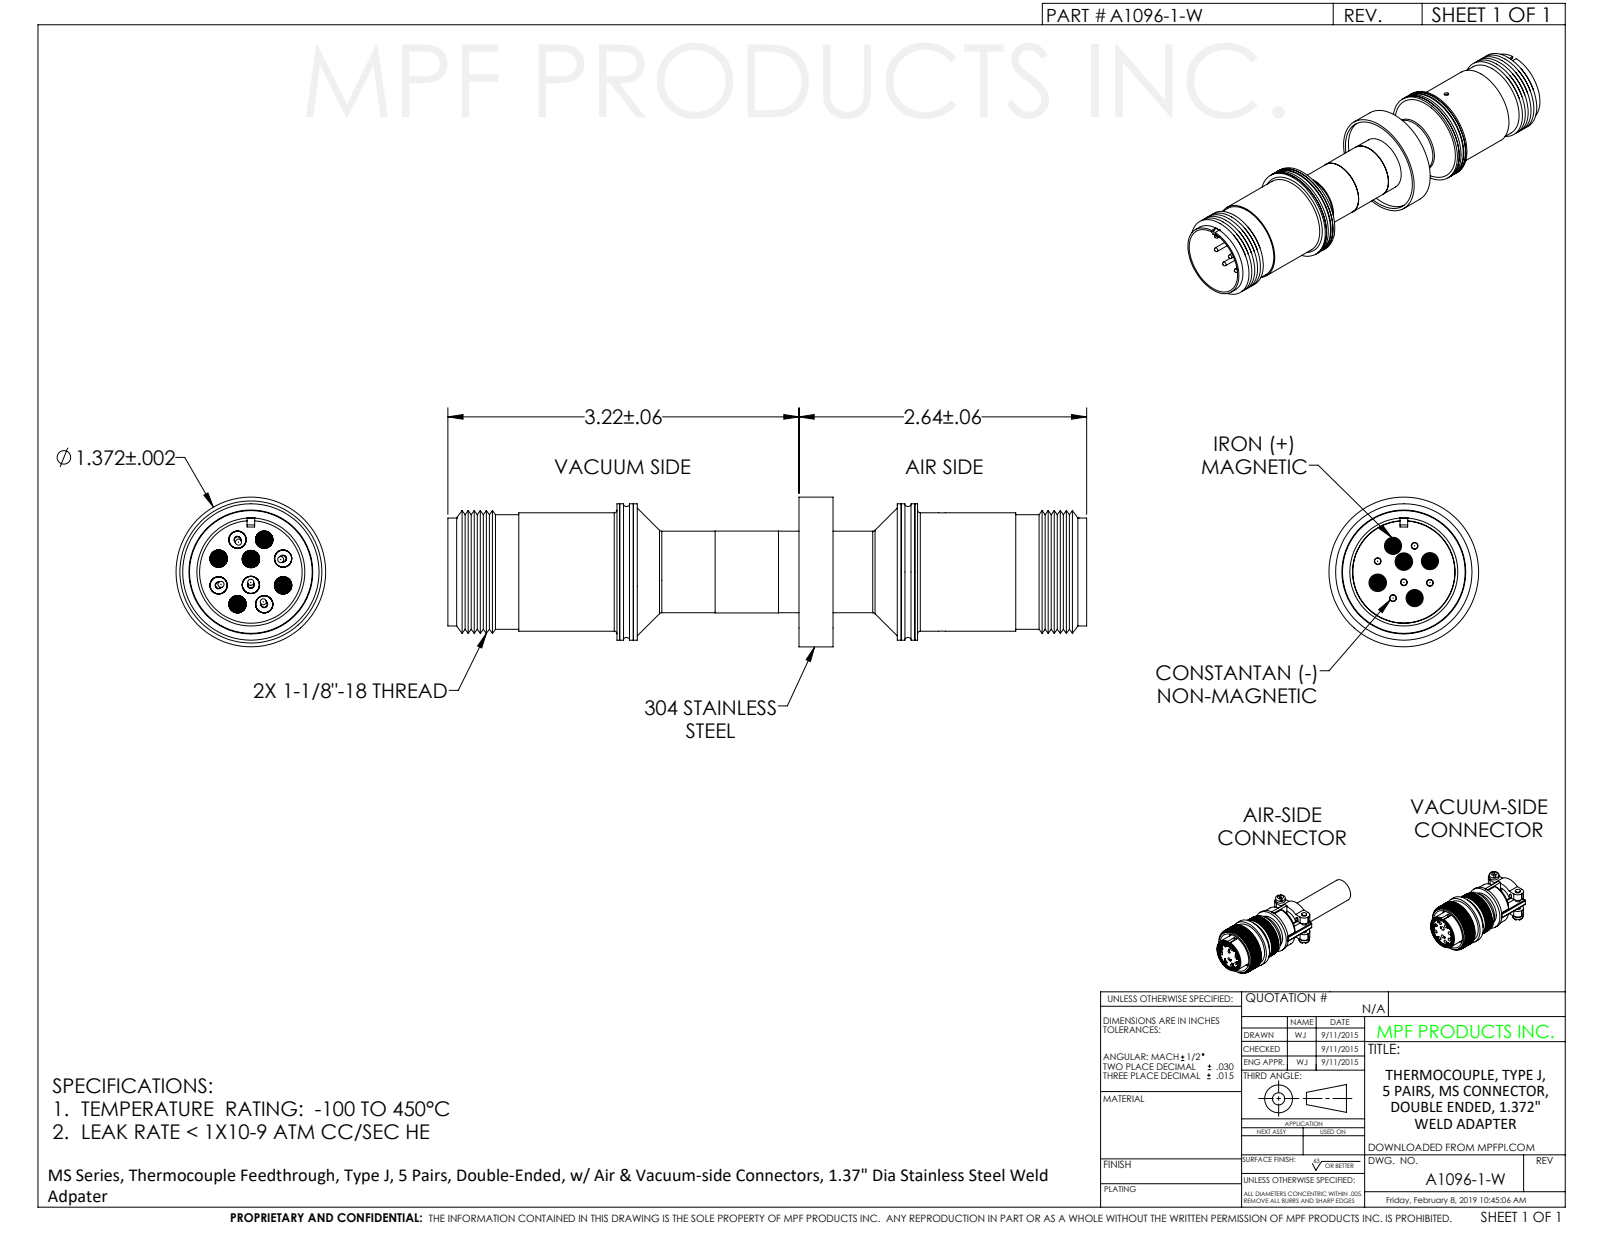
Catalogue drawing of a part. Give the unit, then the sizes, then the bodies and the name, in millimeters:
Units: millimetres
Overall size (bounding box): 148.7 × 34.8 × 34.8
Round holes (diameter × count): ⌀1.6 ×11, ⌀4 ×10, ⌀1.5 ×4, ⌀15.9 ×1, ⌀17.1 ×1, ⌀17.3 ×1, ⌀19.1 ×1, ⌀23.9 ×1, ⌀24.4 ×1, ⌀24.6 ×1, ⌀26.3 ×1, ⌀33.1 ×1
Round bosses / shafts (diameter × count): ⌀1.4 ×48, ⌀4.7 ×10, ⌀4.3 ×10, ⌀34.8 ×1, ⌀31.8 ×1, ⌀27.6 ×1, ⌀26.7 ×1, ⌀26.1 ×1
Partial cylindrical surfaces — rounded edges, fillets, slot ends (radius × count): R0.8 ×16
Main face-to-face distances: 6.4, 25.6, 19.2, 41.8, 35.4, 16.3, 1, 32.4, 54.2, 60.6
Hole centre spacings: 5.8, 10.5, 13.6, 4.8, 1.5, 6.2, 6.6, 8.1
Volume: 33 540 mm³ · Surface area: 42 010 mm²
Bodies: 1 solid, 681 faces (137 planar, 358 cylindrical, 186 other)
Part name (STEP PRODUCT): A1096-1-W
STEP written by: SolidWorks 2012 (CONFIG_CONTROL_DESIGN)
